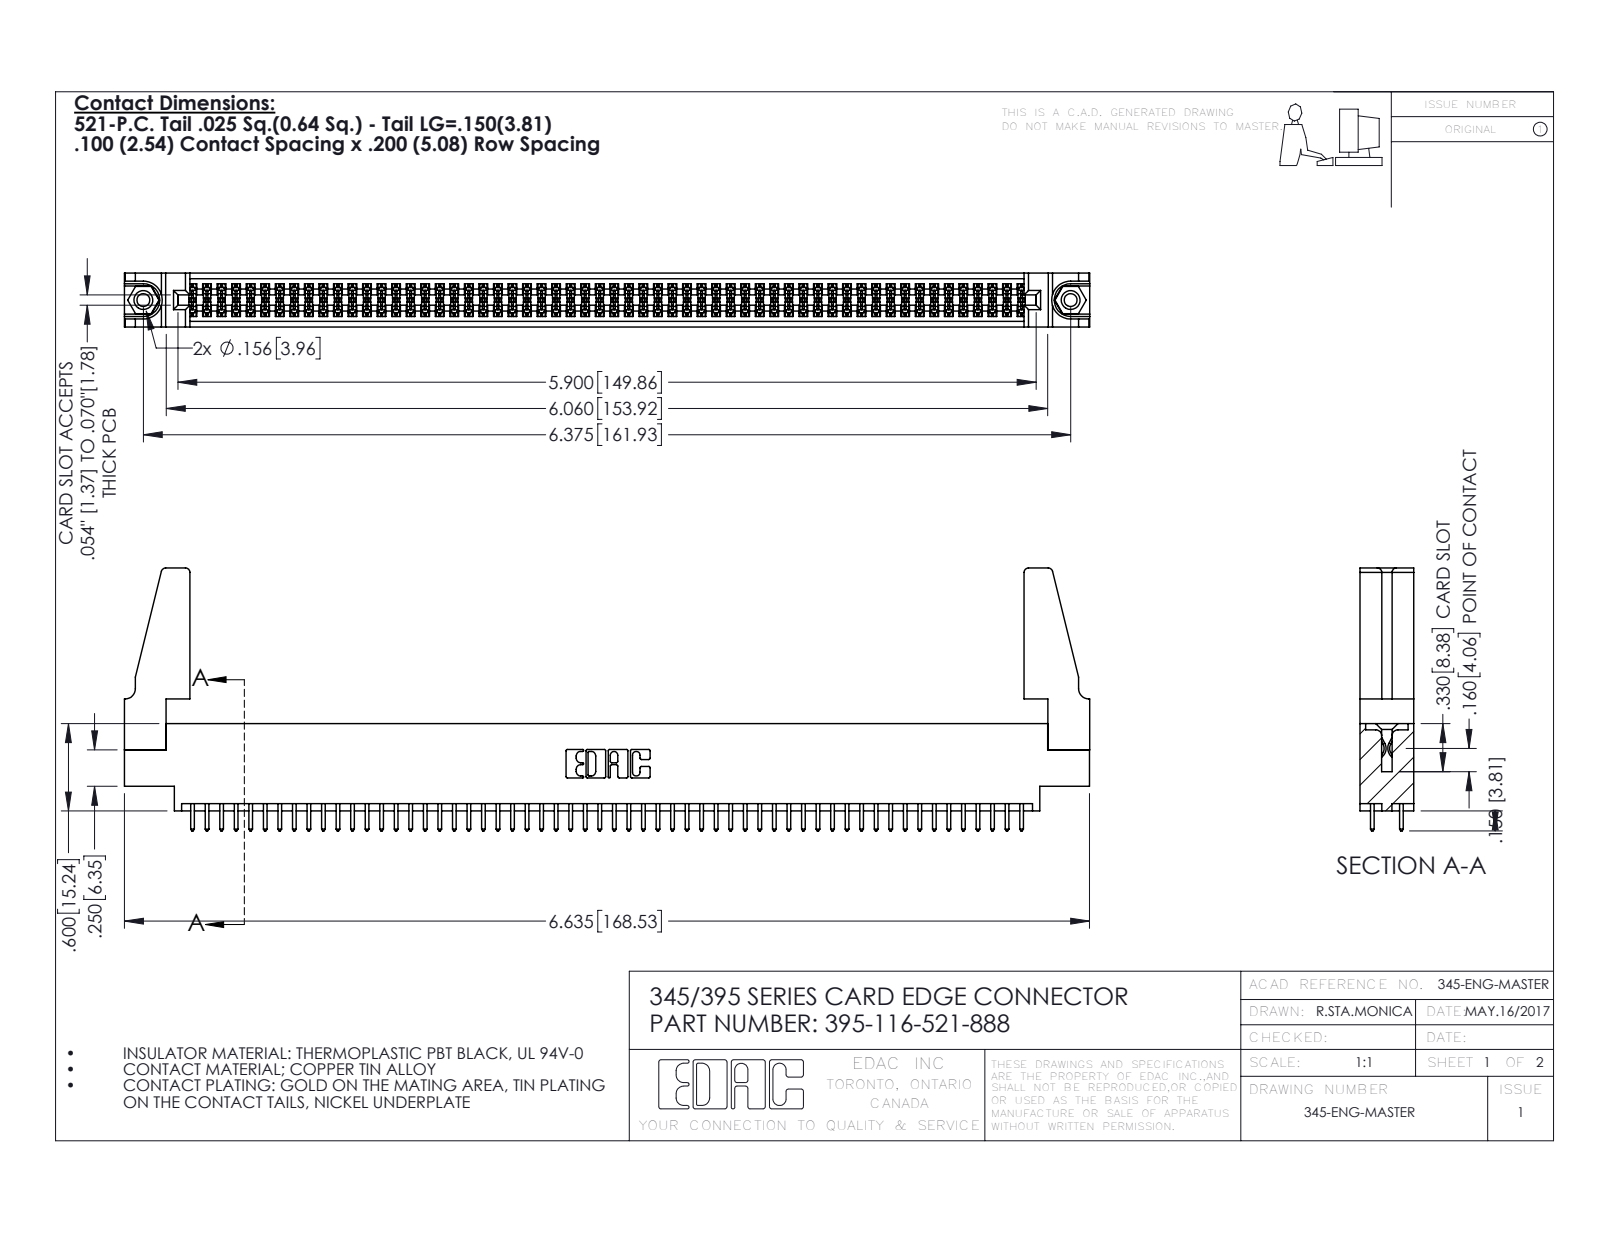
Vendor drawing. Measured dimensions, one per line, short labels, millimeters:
name: 345-250-001_345-250-001-102; 345-292-001_345-293-121; 395-116-521-888; 345 Part_0.170 Offset - 0.156 Dia-TH (+1 more)
written by: SolidWorks 2016 (CONFIG_CONTROL_DESIGN)
unit: mm
bodies: 121 solids, 6054 faces (3984 planar, 2054 cylindrical, 16 other)
size: 168.6 × 45.9 × 9.4
volume: 19 620 mm³; area: 27 450 mm²
holes: 2× ⌀2.3, 2× ⌀3.2, 2× ⌀4, 1× ⌀1.6
bosses: 2× ⌀3.9
rounds: 174× R0.2, 116× R0.3, 22× R0.3, 8× R0.8, 6× R0.2, 6× R0.8, 3× R0.7, 2× R0.4
face distances: 1.8, 7.6, 9.4, 5.1, 2.5, 6.9, 0.6, 5.7, 4.4, 3.8
hole spacings: 6.9, 155.9, 161.9
